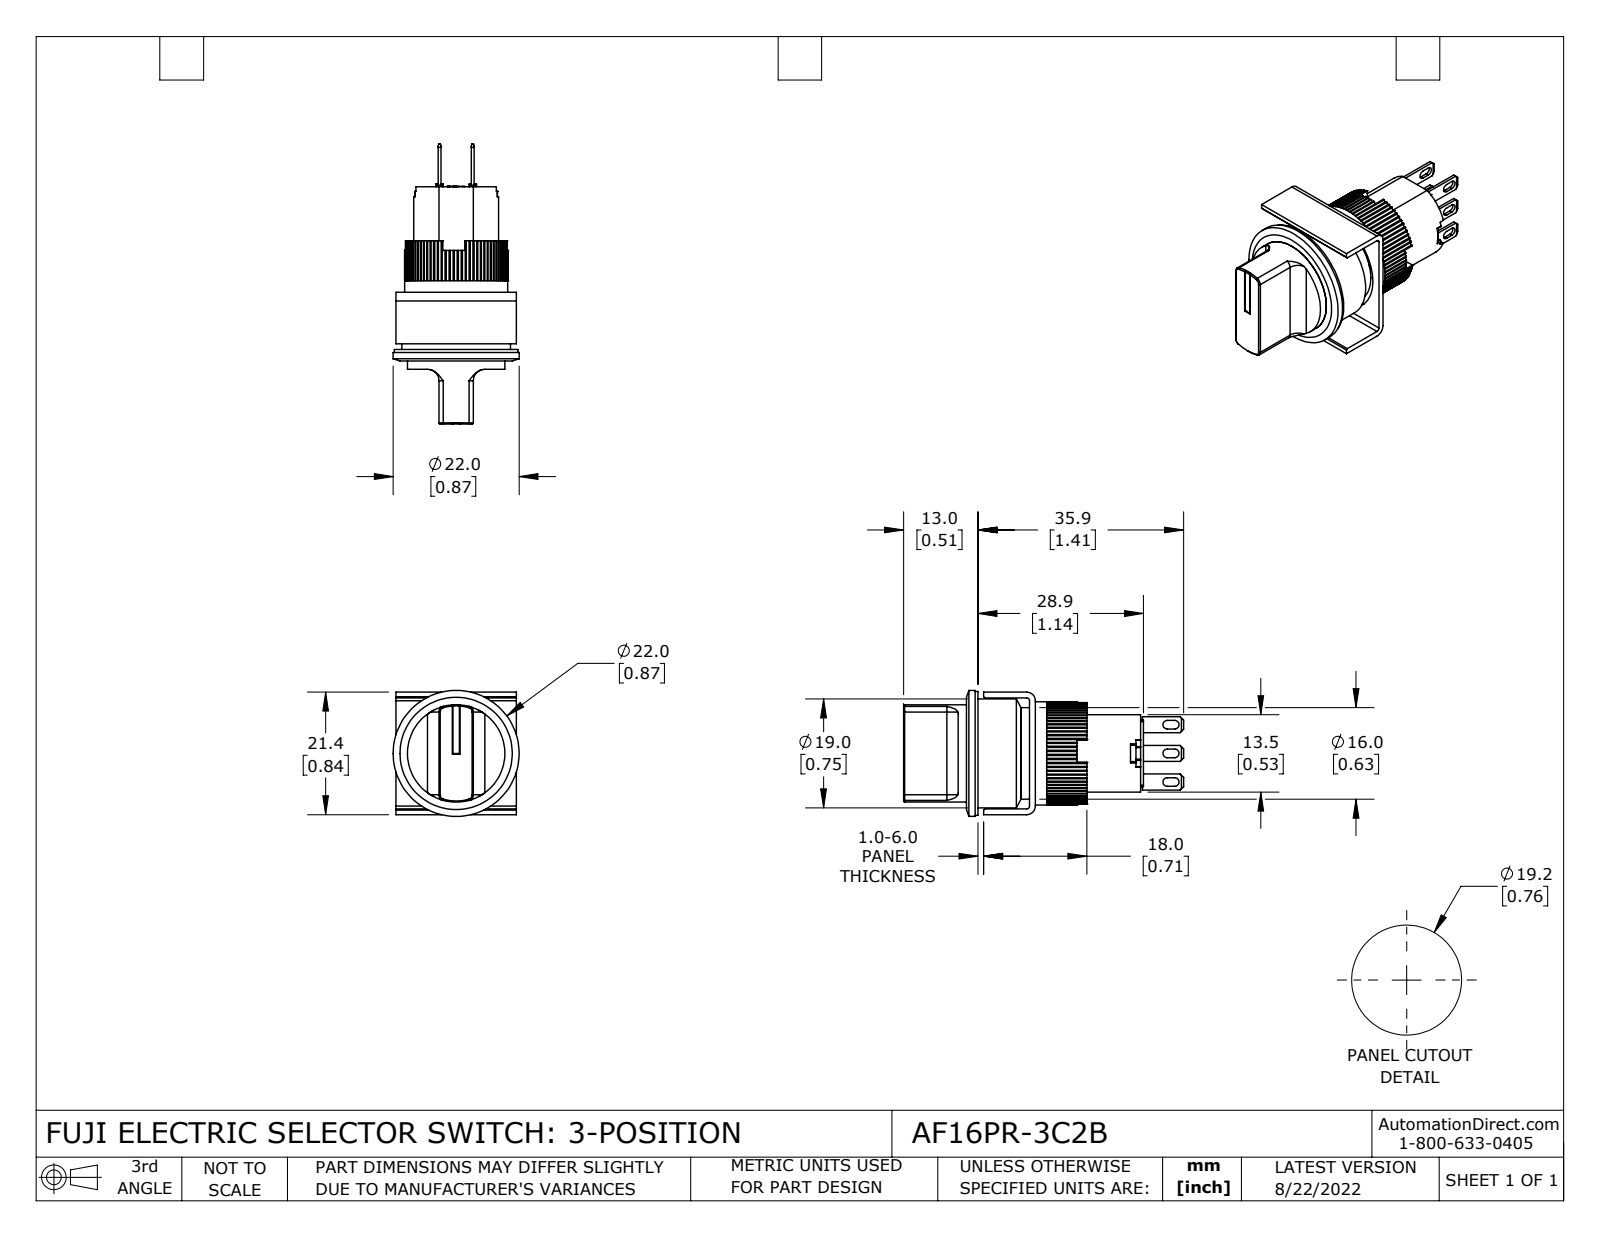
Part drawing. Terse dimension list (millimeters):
name: AF16PR-3C2B
written by: SolidWorks 2021 (CONFIG_CONTROL_DESIGN)
unit: mm
bodies: 12 solids, 709 faces (505 planar, 189 cylindrical, 15 other)
size: 48.9 × 22 × 22
volume: 8 080 mm³; area: 6 716 mm²
holes: 1× ⌀1, 1× ⌀17, 1× ⌀18, 1× ⌀19
bosses: 1× ⌀22, 1× ⌀21.6, 1× ⌀16, 1× ⌀14.8
rounds: 80× R0.3, 14× R0.2, 6× R0.8, 4× R1, 2× R0.5, 2× R1.5, 2× R2, 1× R8.4
face distances: 9.5, 1, 1.5, 20.4, 19.4, 0.5, 11, 3.9, 16.5, 5.9
